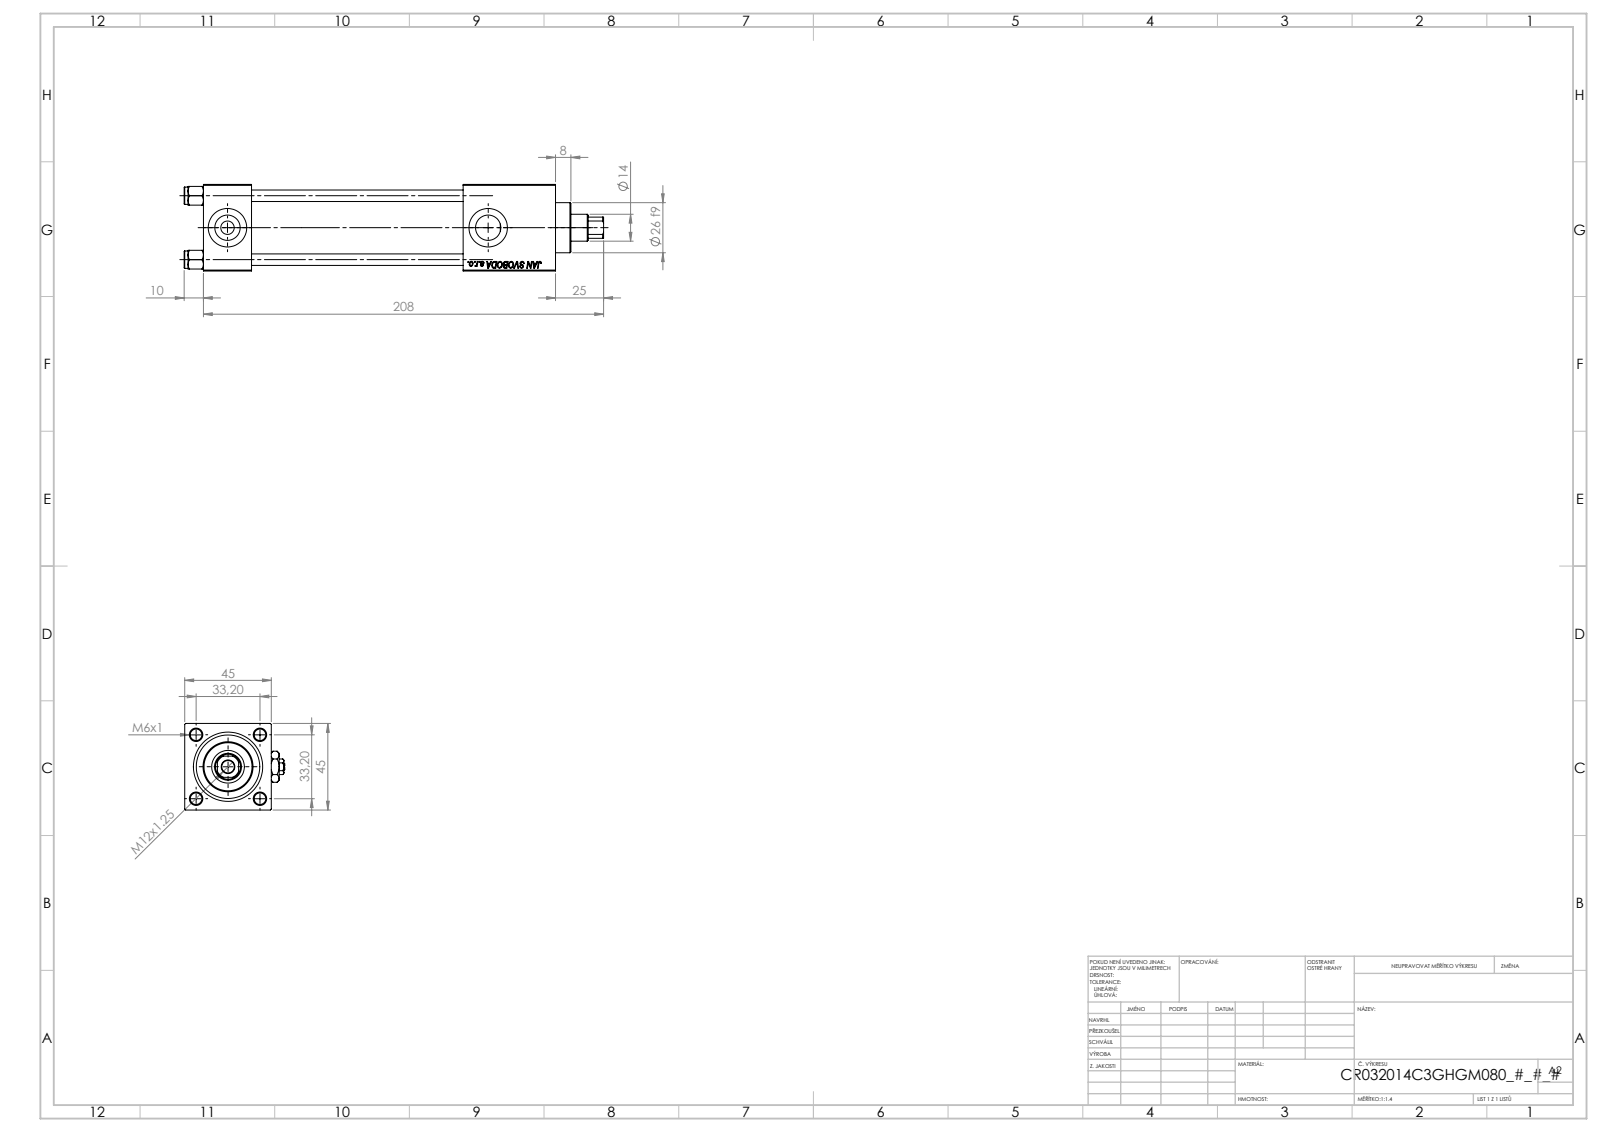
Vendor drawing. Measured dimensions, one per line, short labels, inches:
name: V215_VC_A; V215CR_C_Body; Zatka_pro_OIL_PORT; V215CR_VCP_C (+2 more)
written by: SolidWorks 2019 (CONFIG_CONTROL_DESIGN)
unit: in
bodies: 13 solids, 1248 faces (572 planar, 98 cylindrical, 578 other)
size: 8.583 × 2.047 × 1.772
volume: 13.92 in³; area: 138.4 in²
holes: 4× ⌀0.236, 2× ⌀0.276, 2× ⌀0.518, 2× ⌀0.787, 1× ⌀0.256, 1× ⌀0.551, 1× ⌀0.669, 1× ⌀0.945, 1× ⌀1.26, 1× ⌀1.299
bosses: 4× ⌀0.354, 1× ⌀1.496, 1× ⌀1.024
rounds: 1× R0.256
face distances: 1.772, 0.984, 6.22, 7.205, 5.315, 4.331, 1.89, 6.075, 5.091, 0.76
hole spacings: 0.924, 1.307, 1.848, 5.335
